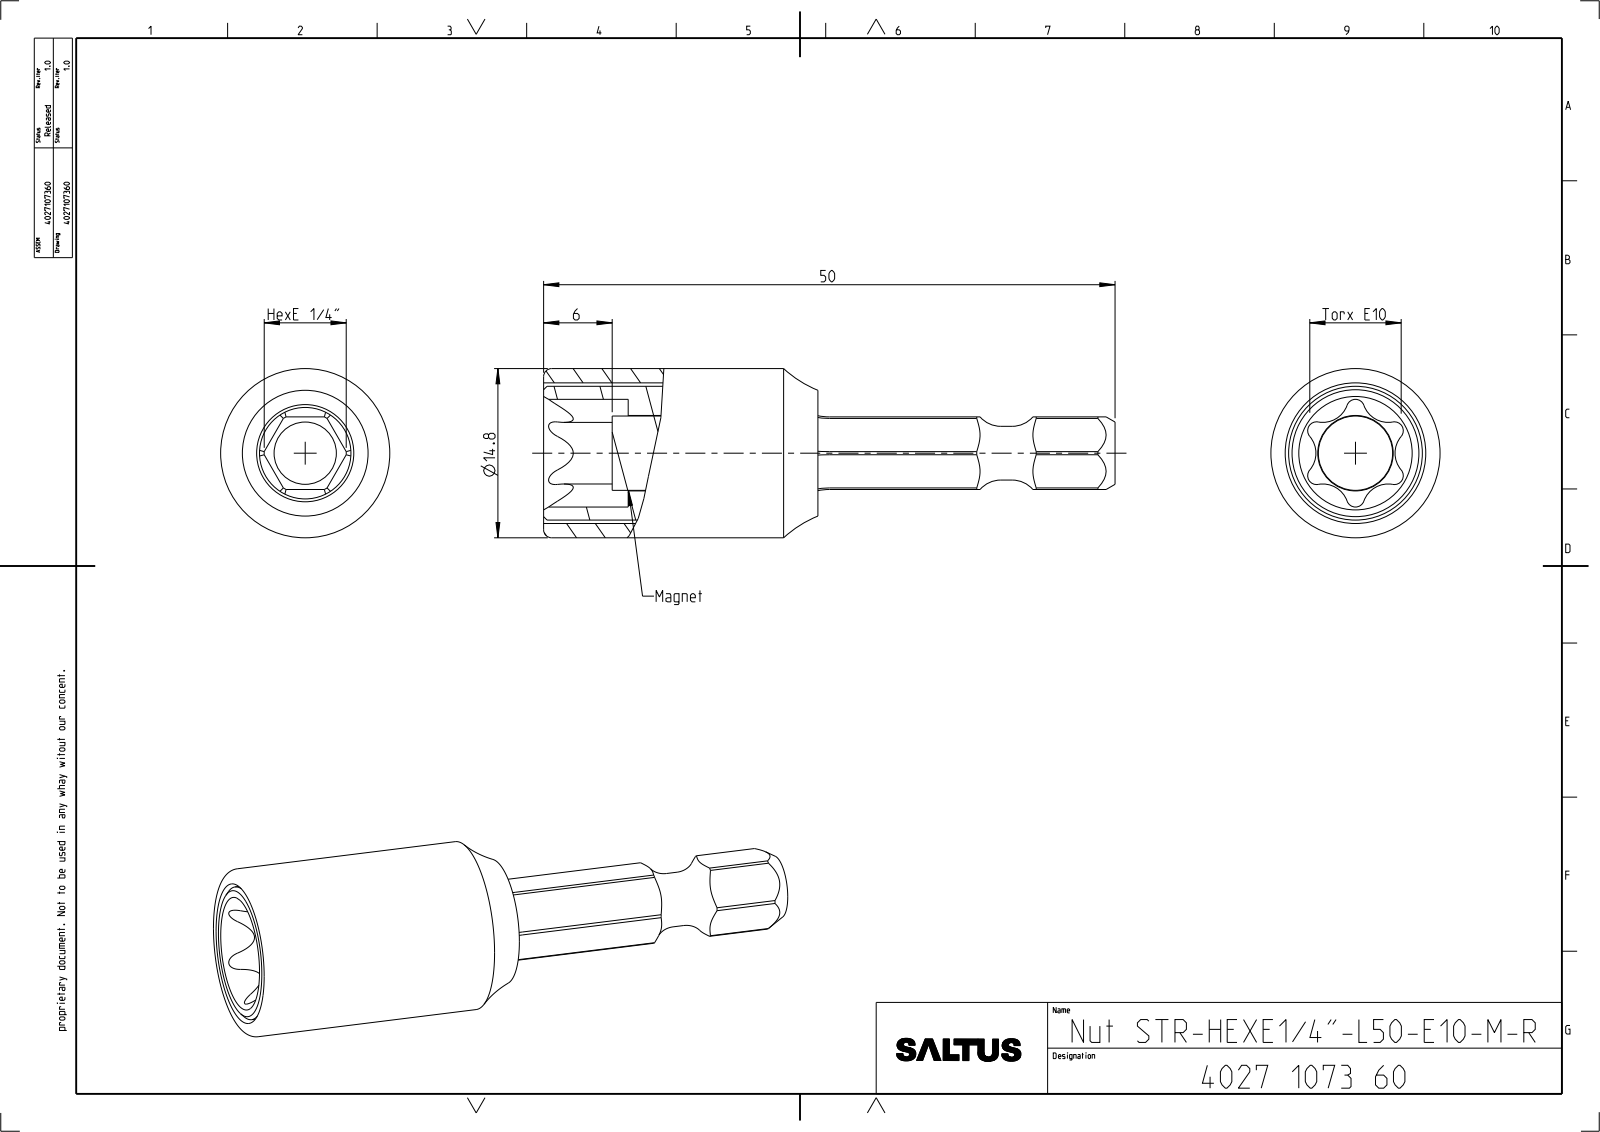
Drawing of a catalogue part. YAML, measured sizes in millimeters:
part_name: "4027911290; 4027043095; 4027107360_ASM"
step_written_by: "CREO PARAMETRIC BY PTC INC, 2022414 (CONFIG_CONTROL_DESIGN)"
units: millimeters
bodies: {solids: 3, faces: 97, planar: 19, cylindrical: 48, other: 30}
overall_size: [50, 14.8, 14.8]
volume: 4008
surface_area: 4249
round_holes:
  - {diameter: 6.6, count: 1}
  - {diameter: 12.3, count: 1}
round_bosses_or_shafts:
  - {diameter: 14.8, count: 1}
  - {diameter: 11.7, count: 1}
  - {diameter: 8, count: 1}
  - {diameter: 6.5, count: 1}
  - {diameter: 4.7, count: 1}
partial_cylinders:
  - {radius: 0.78, count: 6}
  - {radius: 2.26, count: 6}
  - {radius: 5, count: 6}
  - {radius: 3.59, count: 1}
face_to_face_distances: [6.34, 6.36, 24, 10, 18, 8, 14, 6, 26, 36]
